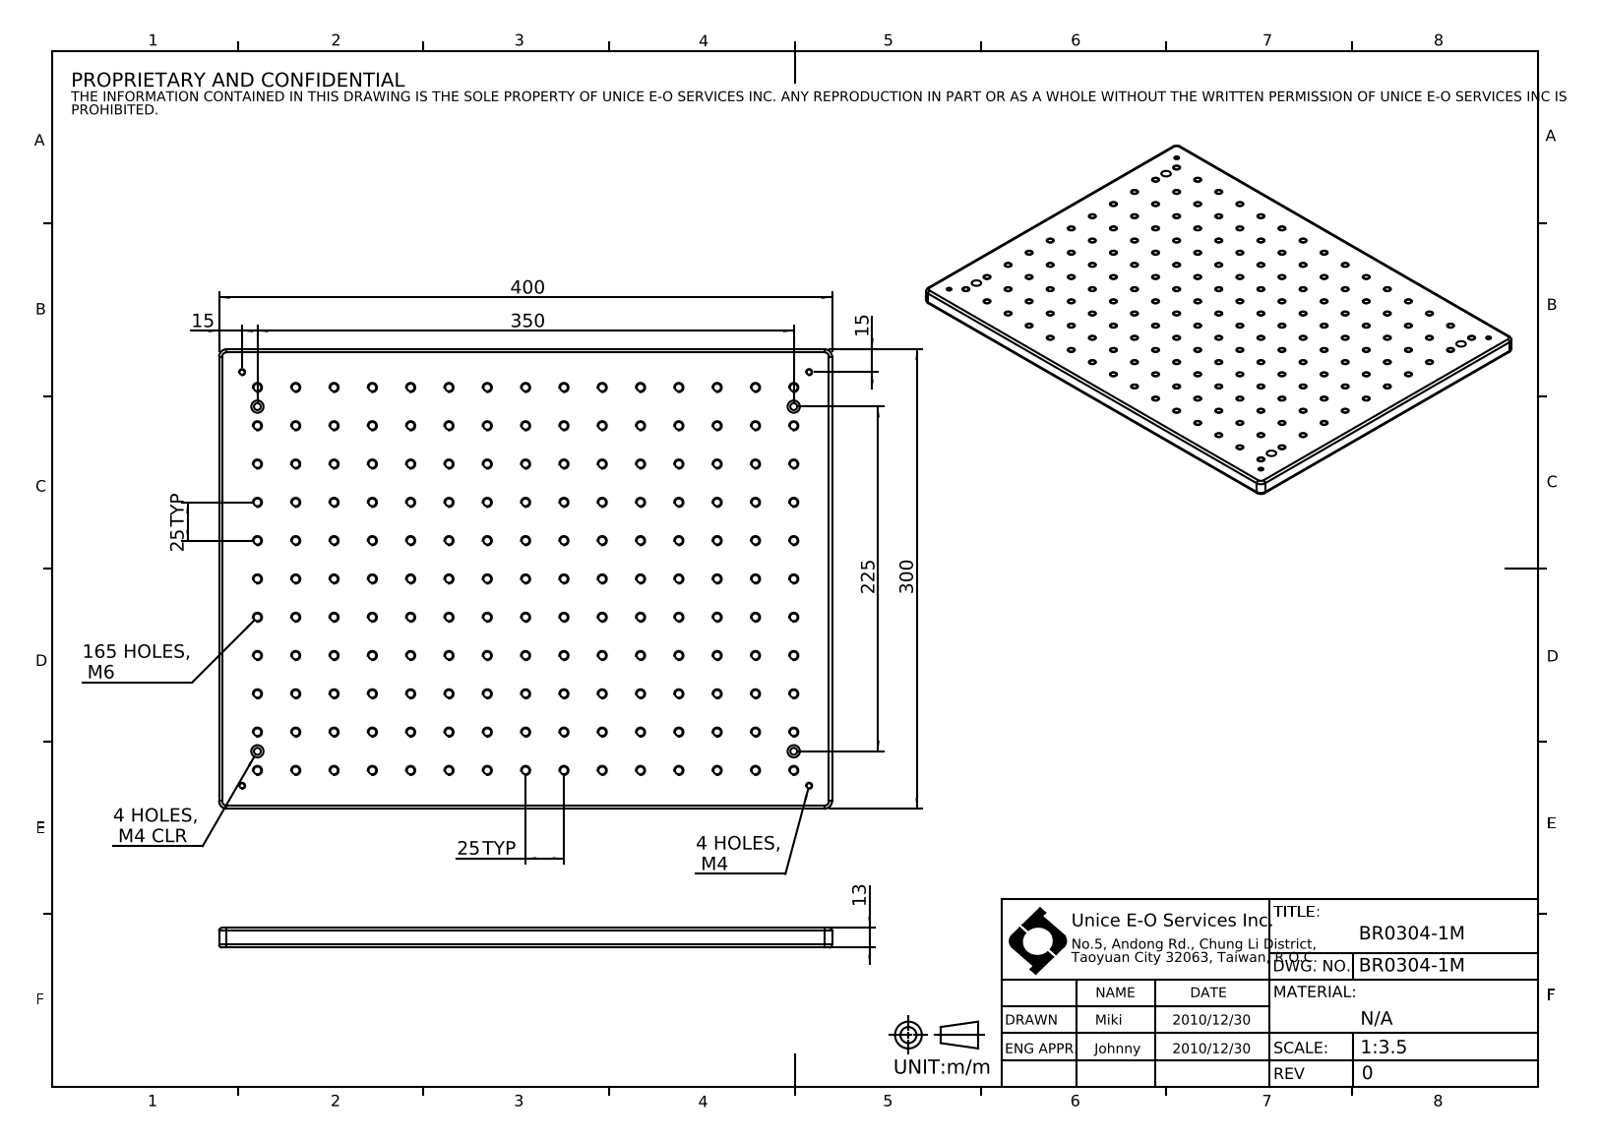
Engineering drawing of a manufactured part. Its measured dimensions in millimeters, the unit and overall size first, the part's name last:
Units: millimetres
Overall size (bounding box): 400 × 300 × 13
Round holes (diameter × count): ⌀5 ×165, ⌀3.3 ×4, ⌀4.5 ×4, ⌀8 ×4
Partial cylindrical surfaces — rounded edges, fillets, slot ends (radius × count): R2 ×8, R5 ×4
Main face-to-face distances: 13, 300, 400, 7, 6
Hole centre spacings: 25, 50, 75, 125, 100, 251.25, 254.95, 250
Volume: 1 513 000 mm³ · Surface area: 284 210 mm²
Bodies: 1 solid, 384 faces (10 planar, 366 cylindrical, 8 other)
Part name (STEP PRODUCT): BR0304-1M
STEP written by: SolidWorks 2016 (CONFIG_CONTROL_DESIGN)
